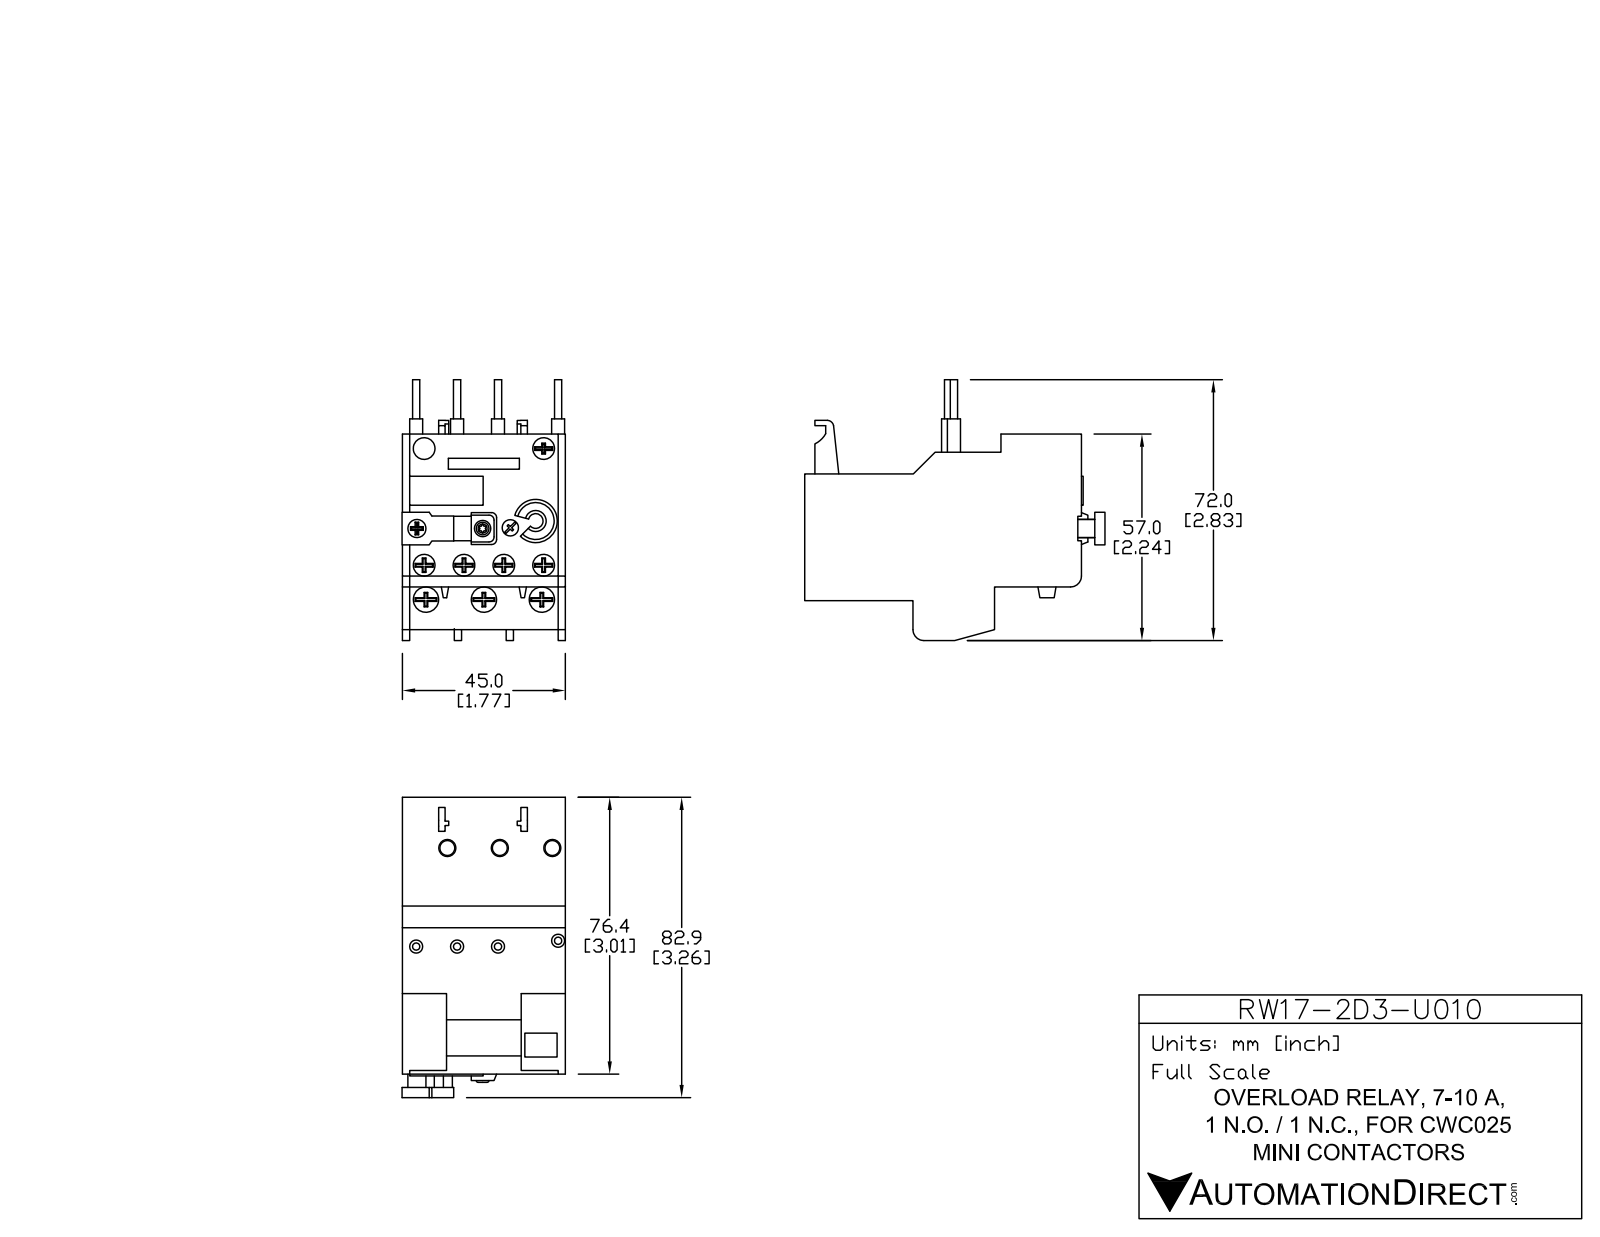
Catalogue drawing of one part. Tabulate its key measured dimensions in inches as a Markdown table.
| quantity | value |
| --- | --- |
| part name | RW17D-2D3-U010 |
| STEP written by | SolidWorks 2013 (AUTOMOTIVE_DESIGN) |
| units | inches |
| bodies | 17 solids, 748 faces (512 planar, 211 cylindrical, 25 other) |
| overall size | 3.254 × 2.776 × 1.793 |
| volume | 7.772 in³ |
| surface area | 53.57 in² |
| round holes (diameter × count) | 0.236 × 6, 0.157 × 3, 0.276 × 3, 0.295 × 3, 0.177 × 1, 0.187 × 1, 0.21 × 1, 0.217 × 1, 0.41 × 1 |
| round bosses / shafts (diameter × count) | 0.217 × 7, 0.118 × 7, 0.069 × 4, 0.22 × 2, 0.128 × 2, 0.253 × 1, 0.242 × 1, 0.187 × 1 |
| partial cylindrical surfaces (radius × count) | 0.02 × 20, 0.01 × 12, 0.039 × 9, 0.178 × 6, 0.231 × 4, 0.309 × 4, 0.059 × 3, 0.049 × 2 |
| main face-to-face distances | 1.791, 0.059, 0.427, 0.433, 3.008, 1.378, 0.056, 2.952, 2.949, 0.236 |
| hole center spacings | 0.591, 0.337, 0.423, 1.181, 0.416, 0.467, 0.561, 0.841 |
